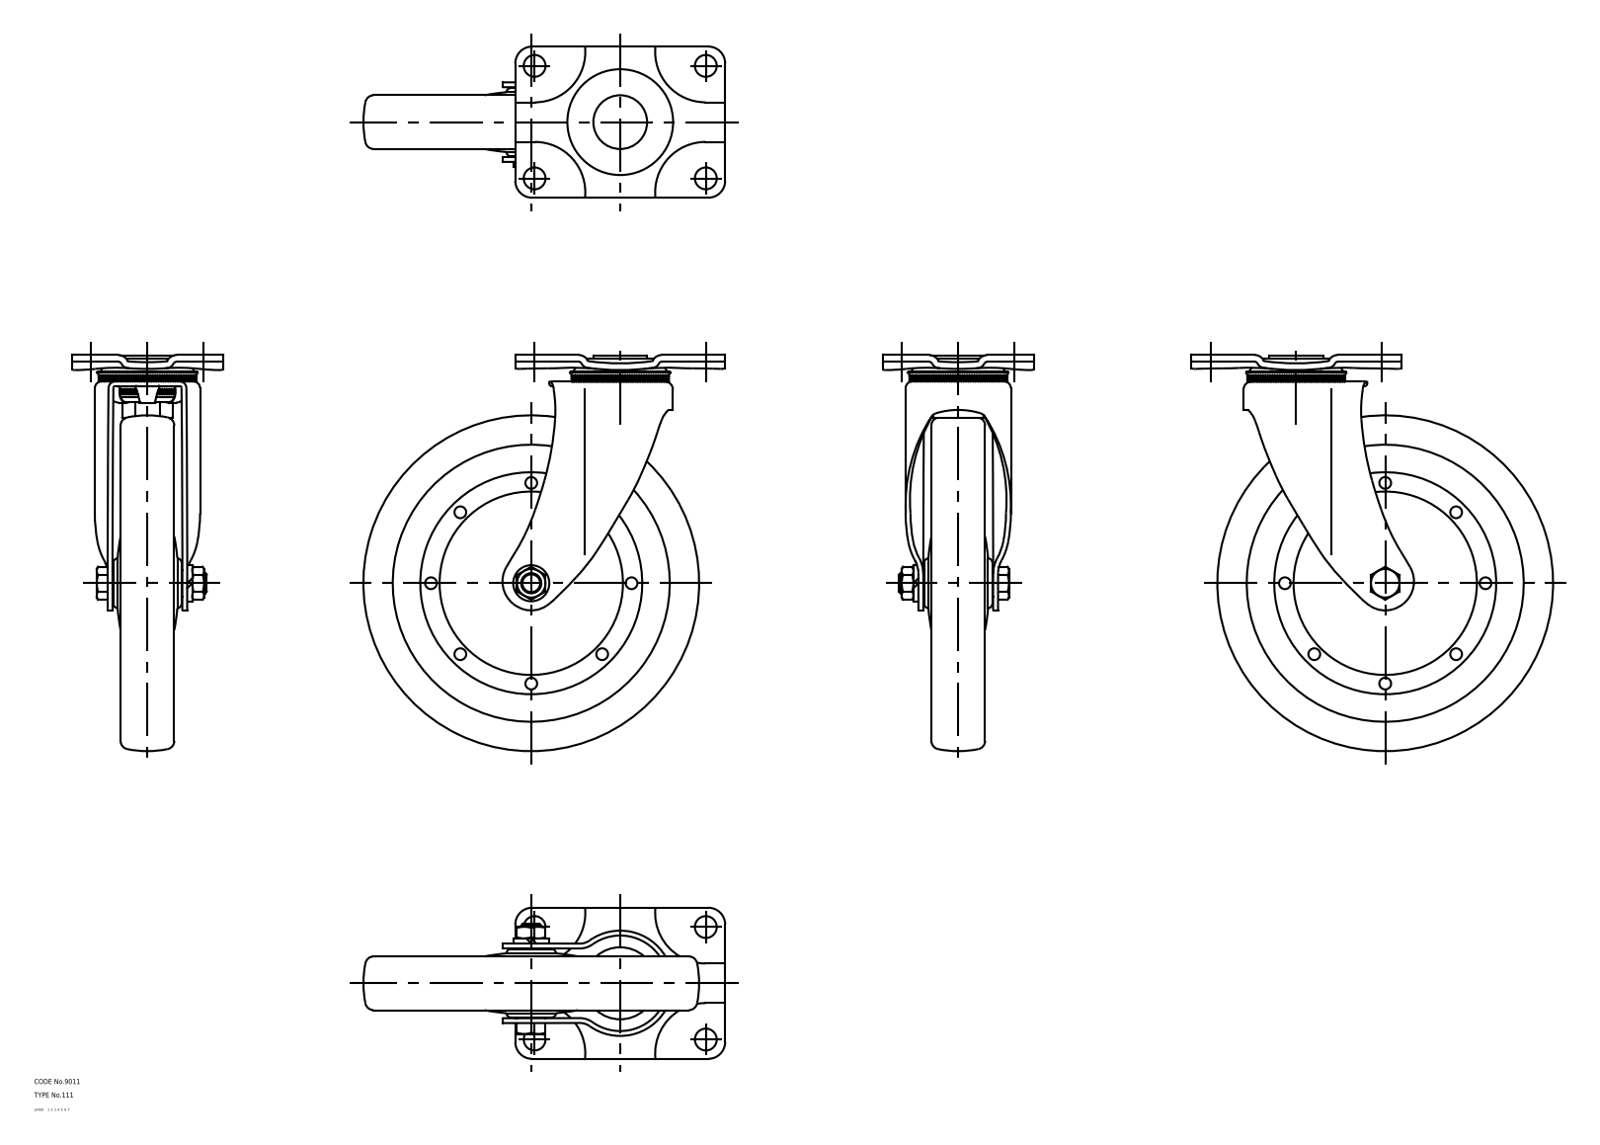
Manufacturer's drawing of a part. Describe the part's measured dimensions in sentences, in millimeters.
The part is named "67143231; 67143244; 67143257; 67143270 (+1 more)". Its 3-D file was written by "CADfix (AUTOMOTIVE_DESIGN)". It is 5 solids with 454 faces: 0 planar, 0 cylindrical and 454 other. Overall it measures 236 by 215.5 by 90 millimeters. Its volume is 1 018 000 cubic millimeters and its surface area 158 503 square millimeters.
